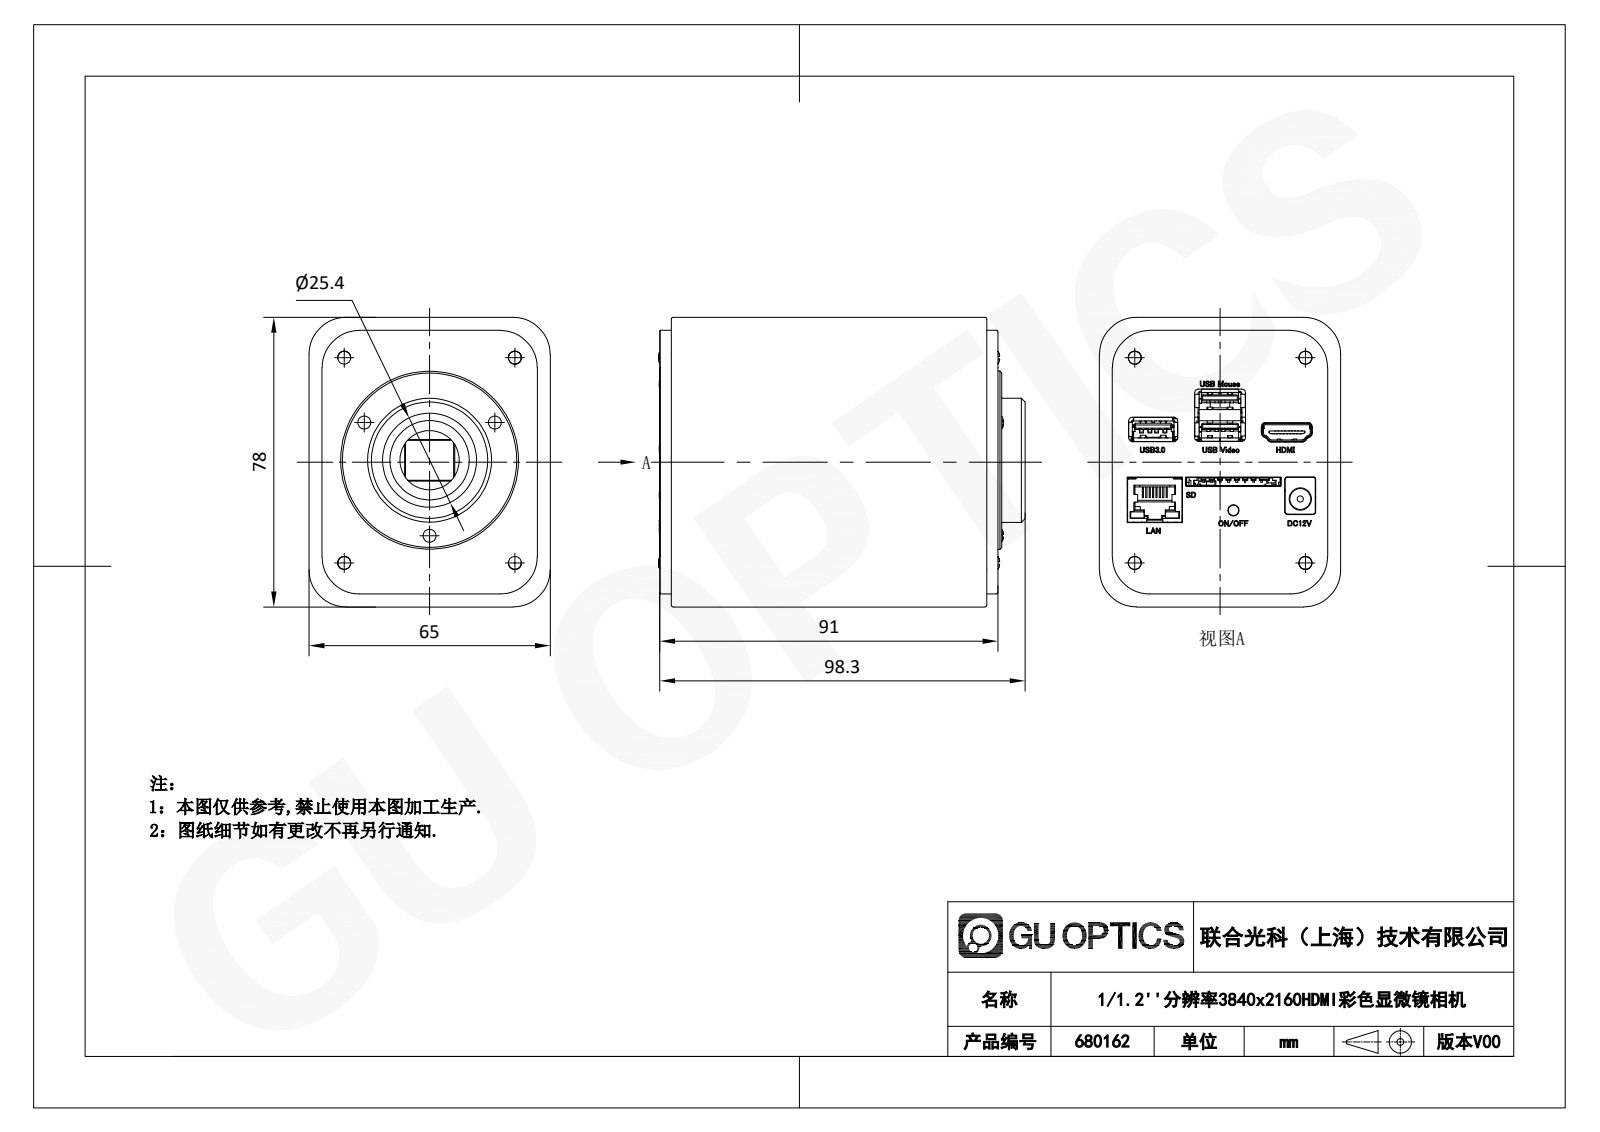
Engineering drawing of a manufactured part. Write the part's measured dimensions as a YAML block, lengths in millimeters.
part_name: "680161"
step_written_by: "SolidWorks 2020 (CONFIG_CONTROL_DESIGN)"
units: millimeters
bodies: {solids: 0, faces: 11634, planar: 7679, cylindrical: 1996, other: 1959}
overall_size: [98.74, 78, 65]
round_holes:
  - {diameter: 1.98, count: 13}
  - {diameter: 1.44, count: 5}
  - {diameter: 2.25, count: 5}
  - {diameter: 0.72, count: 4}
  - {diameter: 3.52, count: 4}
  - {diameter: 3.5, count: 3}
  - {diameter: 1.62, count: 1}
  - {diameter: 2.88, count: 1}
  - {diameter: 3.05, count: 1}
  - {diameter: 3.34, count: 1}
  - {diameter: 5.76, count: 1}
  - {diameter: 16, count: 1}
round_bosses_or_shafts:
  - {diameter: 1.8, count: 15}
  - {diameter: 2, count: 9}
  - {diameter: 3.5, count: 6}
  - {diameter: 3.15, count: 5}
  - {diameter: 2.83, count: 5}
  - {diameter: 1.62, count: 5}
  - {diameter: 3.6, count: 4}
  - {diameter: 4.5, count: 2}
partial_cylinders:
  - {radius: 0.1, count: 177}
  - {radius: 0.18, count: 127}
  - {radius: 0.27, count: 85}
  - {radius: 0.45, count: 82}
  - {radius: 0.14, count: 50}
  - {radius: 0.2, count: 44}
  - {radius: 0.23, count: 23}
  - {radius: 0.9, count: 23}
face_to_face_distances: [0.5, 1.44, 64.5, 7.74, 2.9, 88, 3, 90.9, 65, 64]
hole_center_spacings: [30.6, 3.87, 11.93, 14.54, 19.14, 21.64, 25.91, 26.64]
